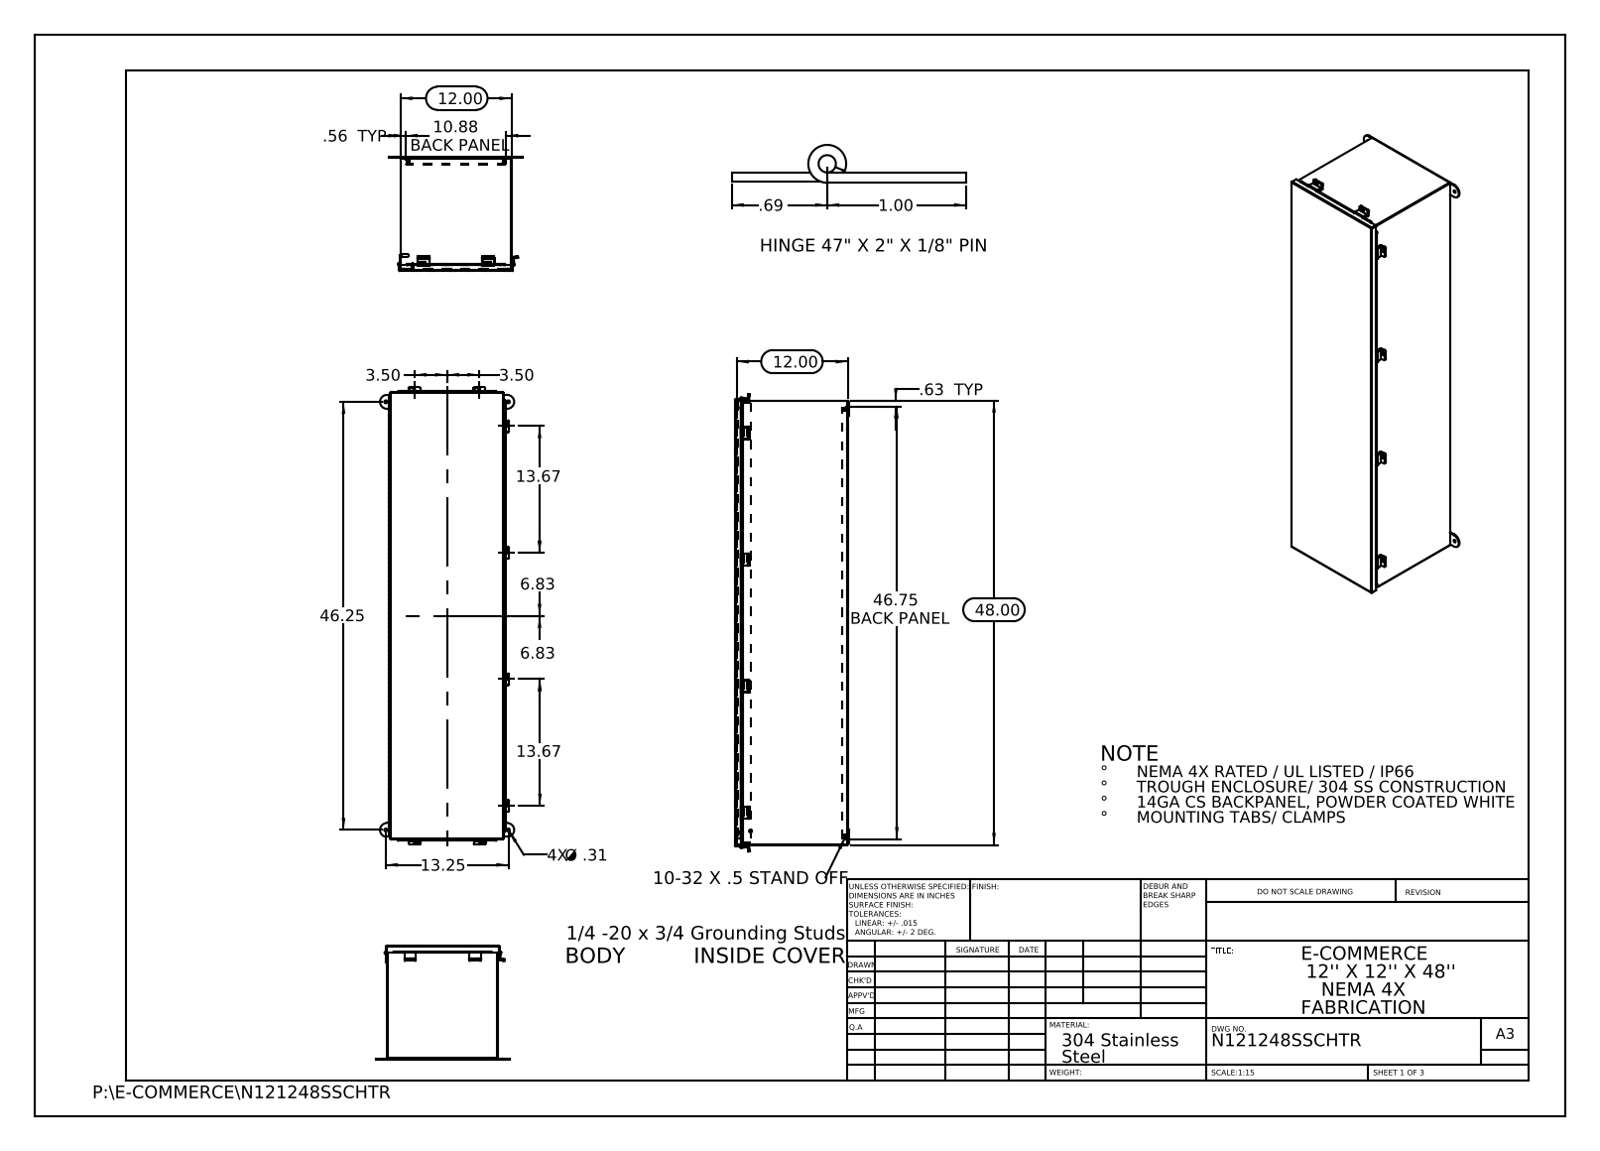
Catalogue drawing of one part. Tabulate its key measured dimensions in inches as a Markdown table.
| quantity | value |
| --- | --- |
| part name | N121248SSCHTR JIC Clamp Bracket; N121248SSCHTR JIC Mounting Bracket; N121248SSCHTR JIC Bottom; N121248SSCHTR (+8 more) |
| STEP written by | SolidWorks 2015 (CONFIG_CONTROL_DESIGN) |
| units | inches |
| bodies | 28 solids, 1467 faces (885 planar, 562 cylindrical, 20 other) |
| overall size | 49.407 × 14.592 × 12.337 |
| volume | 219.6 in³ |
| surface area | 5 855 in² |
| round holes (diameter × count) | 0.25 × 8, 0.313 × 6, 0.125 × 1, 0.375 × 1 |
| round bosses / shafts (diameter × count) | 0.315 × 2, 0.236 × 2, 0.273 × 1, 0.25 × 1 |
| partial cylindrical surfaces (radius × count) | 0.125 × 30, 0.133 × 16, 0.009 × 12, 0.013 × 11, 0.088 × 11, 0.083 × 6, 0.1 × 6, 0.75 × 6 |
| main face-to-face distances | 0.075, 11.925, 12.128, 12, 11.85, 12.203, 12.053, 47.925, 47.85, 48 |
| hole center spacings | 23.125, 13.25, 7, 13.666, 26.606, 26.698, 27.332, 46.25 |
